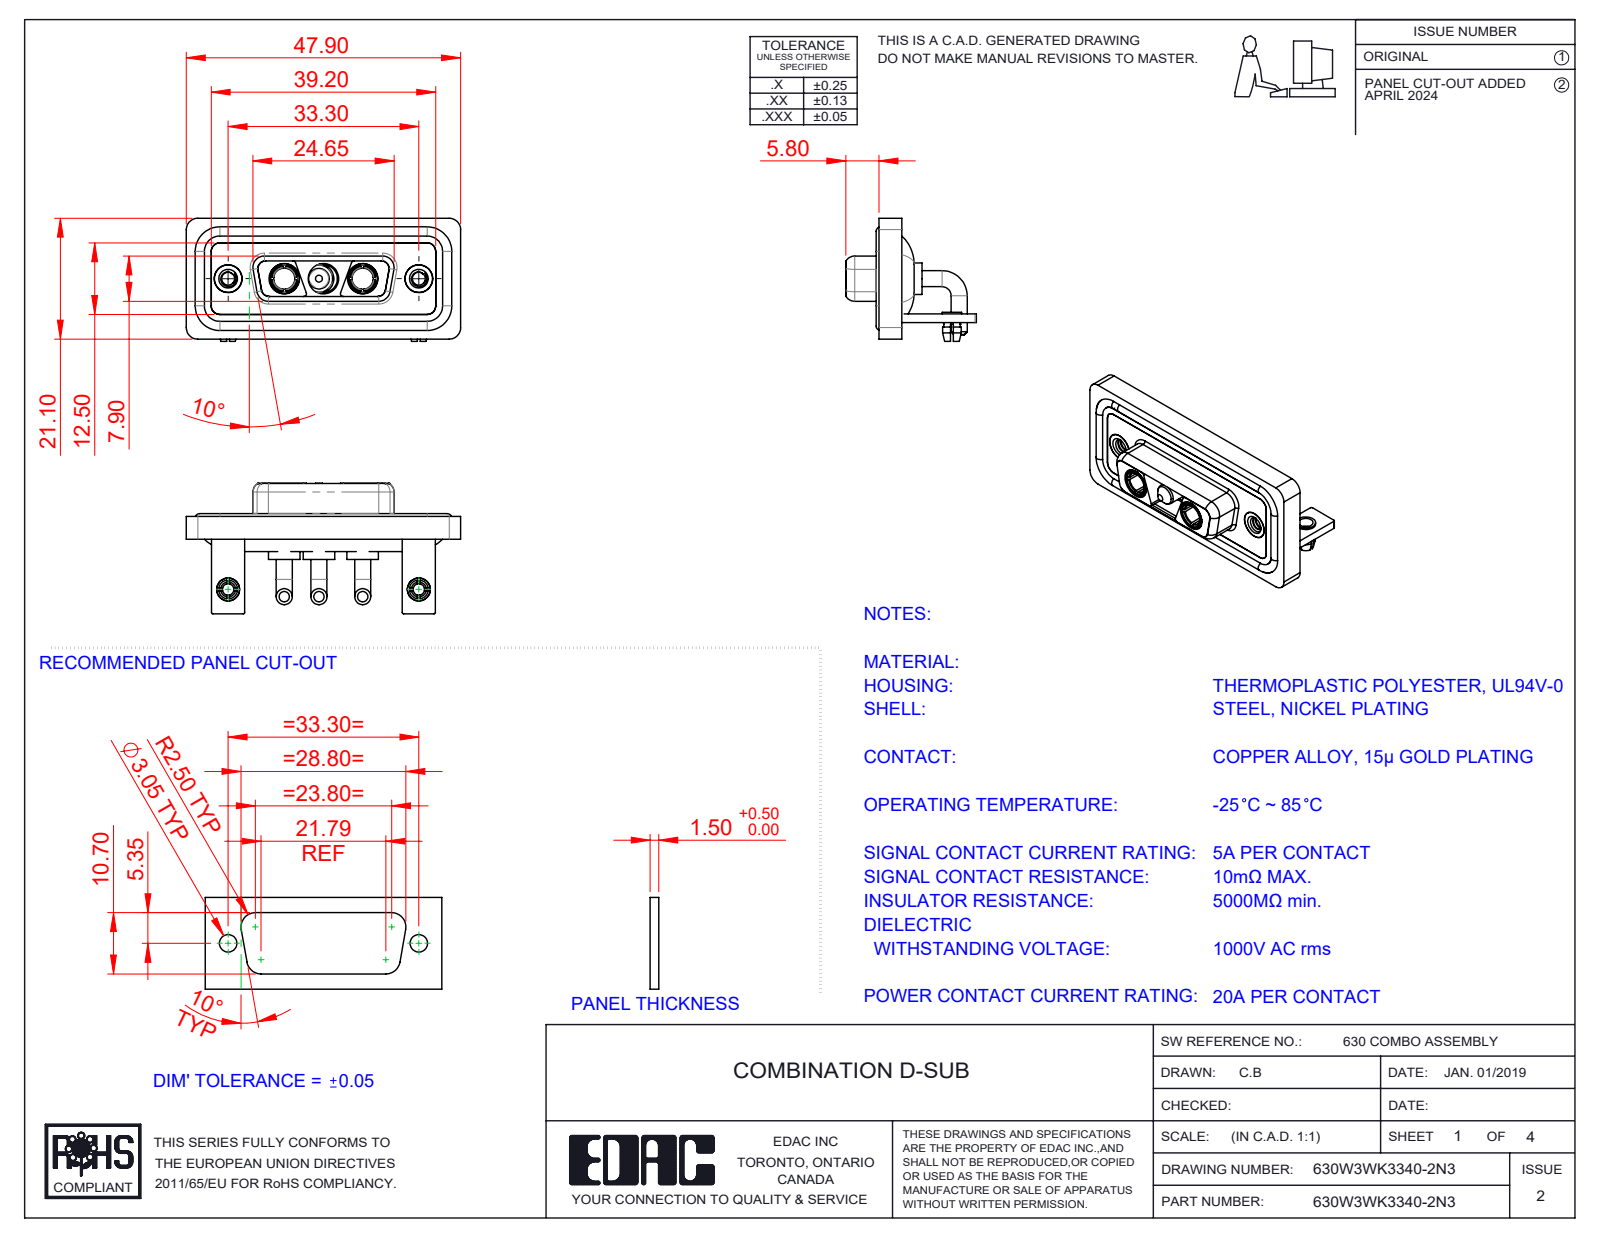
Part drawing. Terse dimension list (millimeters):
name: 630Combo Stabilizer Bracket_50 Contacts; 630Combo Housing_3WK3; 630Combo Board Lock_50 Contacts; Power Pin_20A RA (+6 more)
written by: SolidWorks 2023 (CONFIG_CONTROL_DESIGN)
unit: mm
bodies: 17 solids, 735 faces (246 planar, 320 cylindrical, 169 other)
size: 47.9 × 22.8 × 21.5
volume: 6 435 mm³; area: 10 684 mm²
holes: 5× ⌀4.85, 3× ⌀5.3, 2× ⌀2, 2× ⌀2.26, 2× ⌀2.5, 2× ⌀3.2, 2× ⌀3.7, 2× ⌀4, 2× ⌀4.05, 2× ⌀5
bosses: 6× ⌀2.8, 4× ⌀1.6, 3× ⌀5.5, 3× ⌀5.2, 3× ⌀4.75, 3× ⌀3.75, 2× ⌀4.96, 2× ⌀4.95
rounds: 21× R2, 18× R1.5, 16× R0.25, 12× R1.35, 9× R0.5, 8× R1.6, 4× R0.6, 4× R0.65
face distances: 0.4, 2.9, 1.5, 3.7, 1.8, 1.1, 4.1, 1.6, 2.5, 1.4
hole spacings: 6.85, 9.8, 16.65, 23.5, 33.3, 13.7
